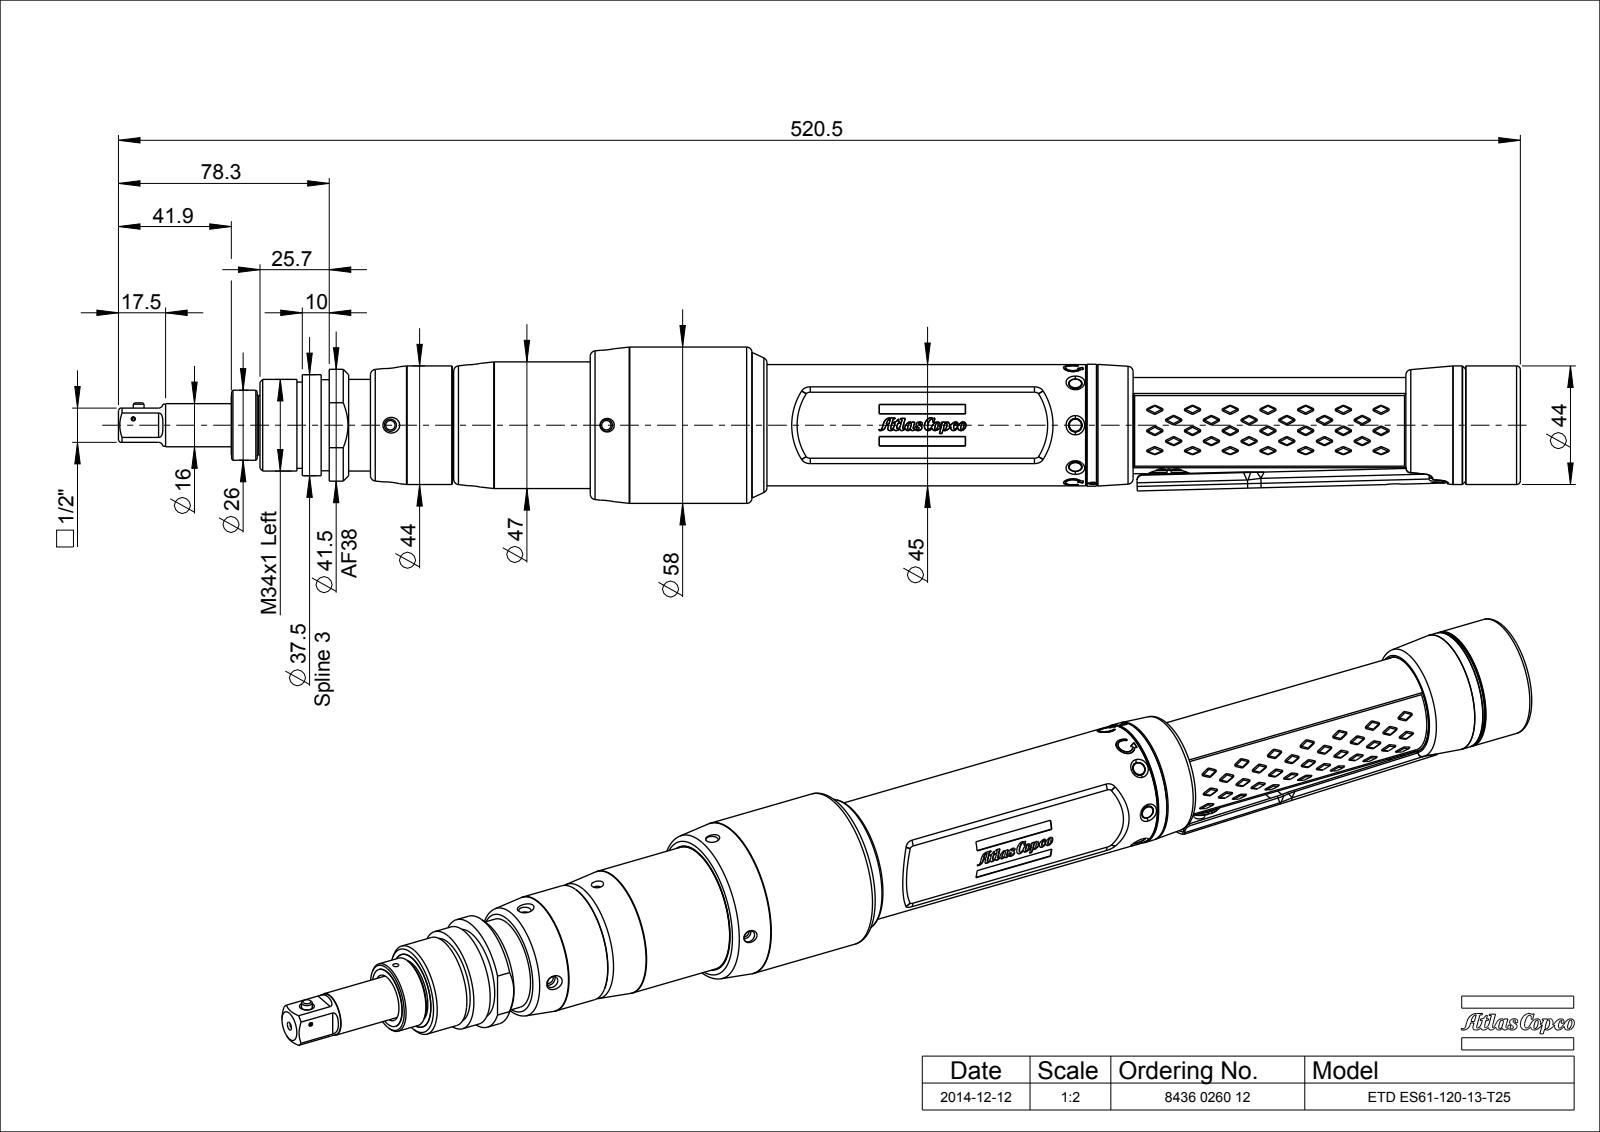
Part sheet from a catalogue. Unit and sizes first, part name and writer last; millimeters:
Units: millimetres
Overall size (bounding box): 520.45 × 58 × 58
Round holes (diameter × count): ⌀2.64 ×12, ⌀3.27 ×12, ⌀3.6 ×12, ⌀4.2 ×6, ⌀4.5 ×6, ⌀2.5 ×5, ⌀5 ×5, ⌀2 ×3, ⌀0.9 ×1, ⌀1.5 ×1, ⌀2.2 ×1, ⌀2.6 ×1
Round bosses / shafts (diameter × count): ⌀2.2 ×9, ⌀1.9 ×9, ⌀1.57 ×9, ⌀3.2 ×7, ⌀2.92 ×3, ⌀3.05 ×2, ⌀2.54 ×2, ⌀2.3 ×2
Partial cylindrical surfaces — rounded edges, fillets, slot ends (radius × count): R0.2 ×60, R0.4 ×26, R2 ×24, R1 ×22, R0.5 ×14, R0.1 ×12, R0.25 ×10, R0.24 ×6
Main face-to-face distances: 1, 1.5, 13.7, 311.4, 32.3, 10, 146, 10.5, 38.6, 12.7
Hole centre spacings: 6.2, 9.51, 14.67, 19.64, 23.72, 5.88, 13.44, 14.5
Volume: 346 100 mm³ · Surface area: 282 563 mm²
Bodies: 45 solids, 6155 faces (2544 planar, 934 cylindrical, 2677 other)
Part name (STEP PRODUCT): 4220388170_AF0; 4220388112_AF0; 4220388172_AF0_ASM; 4220388180_ASM (+8 more)
STEP written by: PRO/ENGINEER BY PARAMETRIC TECHNOLOGY CORPORATION, 2013410 (CONFIG_CONTROL_DESIGN)
